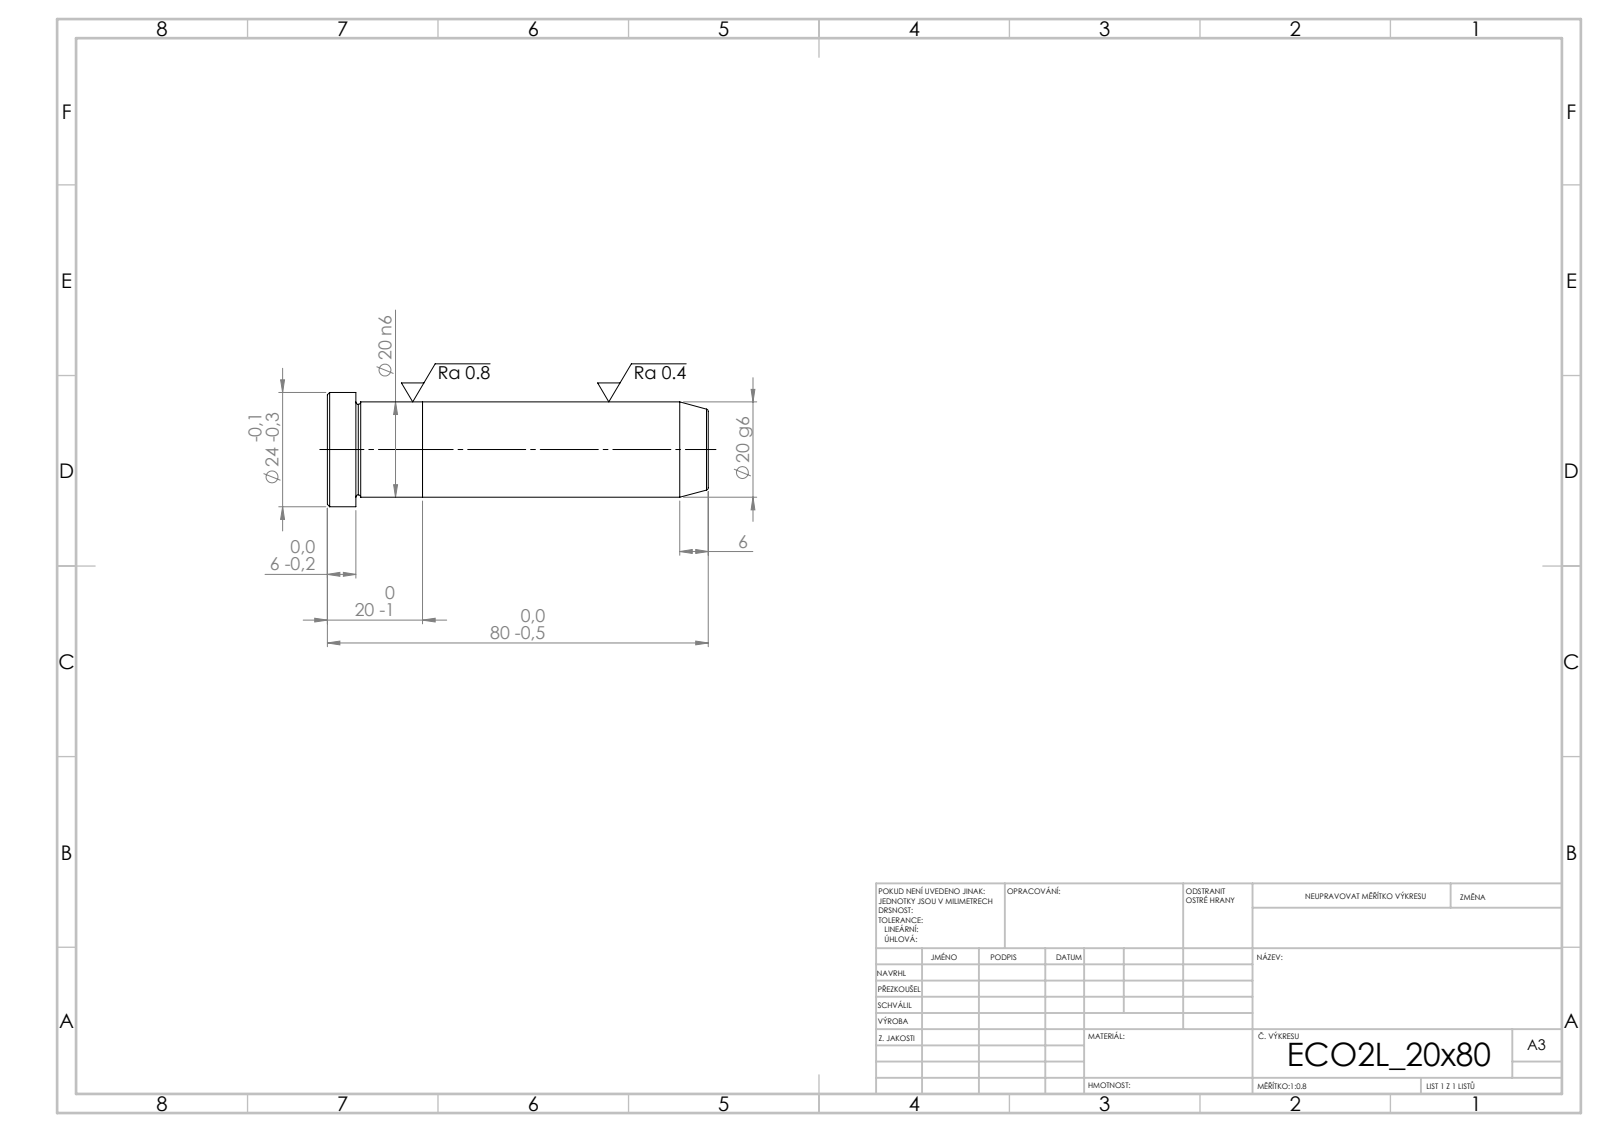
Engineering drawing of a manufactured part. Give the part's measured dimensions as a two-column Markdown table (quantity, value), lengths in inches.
| quantity | value |
| --- | --- |
| STEP written by | SolidWorks 2019 (CONFIG_CONTROL_DESIGN) |
| units | inches |
| bodies | 2 solids, 21 faces (5 planar, 6 cylindrical, 10 other) |
| overall size | 3.15 × 0.945 × 0.945 |
| volume | 1.565 in³ |
| surface area | 10.12 in² |
| round bosses / shafts (diameter × count) | 0.945 × 1, 0.787 × 1 |
| main face-to-face distances | 0.787, 2.362, 3.15, 2.913, 0.551, 0.236 |
